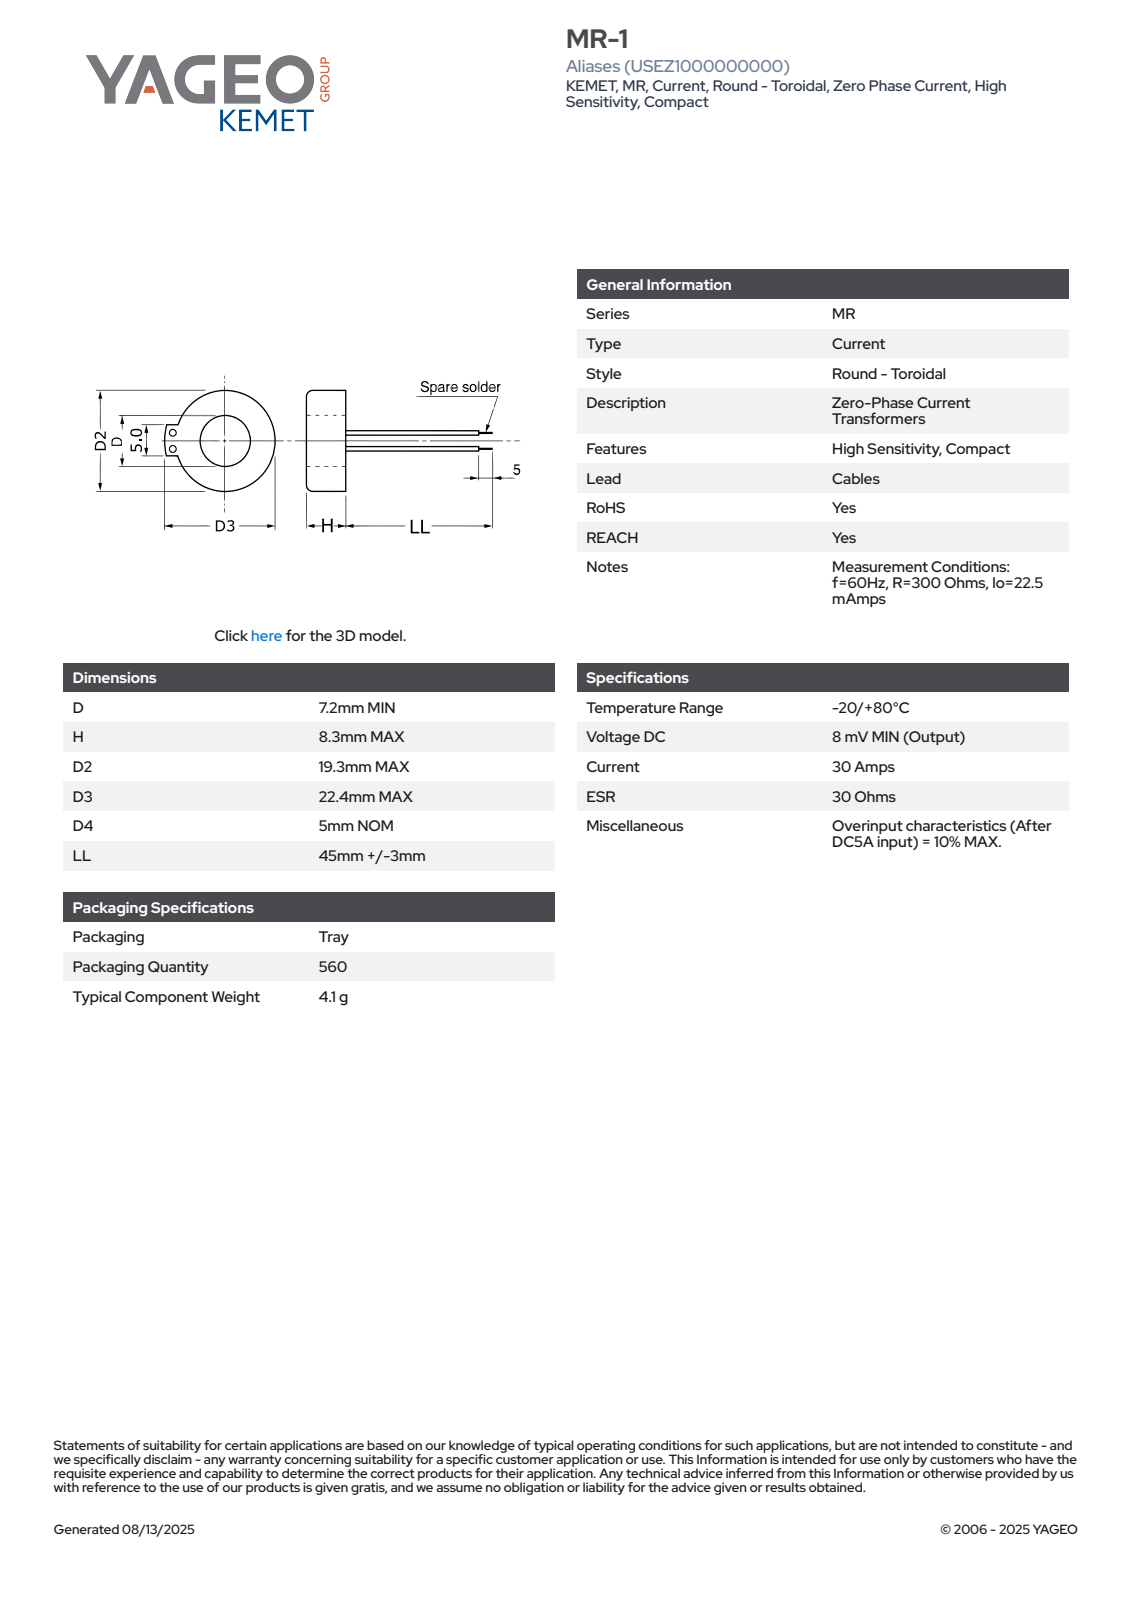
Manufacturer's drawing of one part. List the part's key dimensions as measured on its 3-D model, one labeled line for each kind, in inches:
Part name (STEP PRODUCT): SC_MR1_D7.2H8.3D219.3D322.4D45LL48
STEP written by: SolidWorks 2014 (AUTOMOTIVE_DESIGN)
Units: inches
Bodies: 1 solid, 84 faces (30 planar, 18 cylindrical, 36 other)
Overall size (bounding box): 2.217 × 0.882 × 0.76
Volume: 0.139 in³ · Surface area: 2.387 in²
Round holes (diameter × count): ⌀0.283 ×1
Round bosses / shafts (diameter × count): ⌀0.039 ×2, ⌀0.026 ×2, ⌀0.76 ×1
Partial cylindrical surfaces — rounded edges, fillets, slot ends (radius × count): R0.039 ×2, R0.38 ×1
Main face-to-face distances: 0.327, 0.197, 1.693, 2.02, 1.89, 2.217, 0.124, 0.203, 2.093, 1.896
